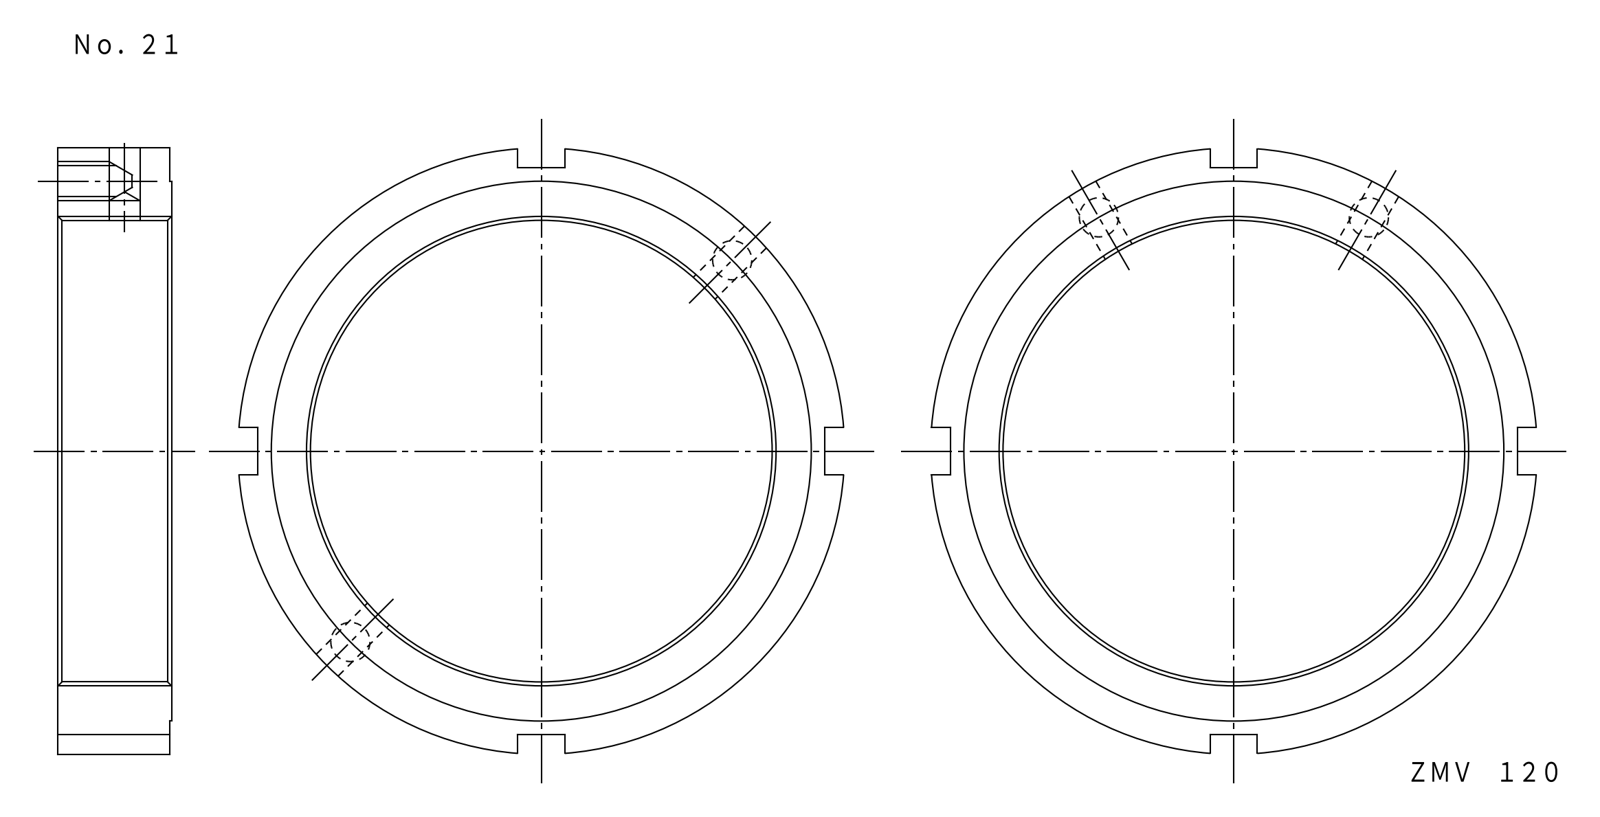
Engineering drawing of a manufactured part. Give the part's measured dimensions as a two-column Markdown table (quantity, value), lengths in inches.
| quantity | value |
| --- | --- |
| part name | FKD ZMV120 |
| STEP written by | Autodesk Inventor LT (CONFIG_CONTROL_DESIGN) |
| units | inches |
| bodies | 1 solid, 29 faces (15 planar, 10 cylindrical, 4 other) |
| overall size | 6.084 × 6.084 × 1.142 |
| volume | 12.65 in³ |
| surface area | 65.03 in² |
| round holes (diameter × count) | 0.311 × 2, 0.33 × 2, 4.724 × 1 |
| round bosses / shafts (diameter × count) | 6.102 × 1, 5.433 × 1 |
| main face-to-face distances | 1.122, 0.02, 1.142, 2.618, 3.091, 5.709, 0.472 |
| hole center spacings | 2.717, 5.433 |
